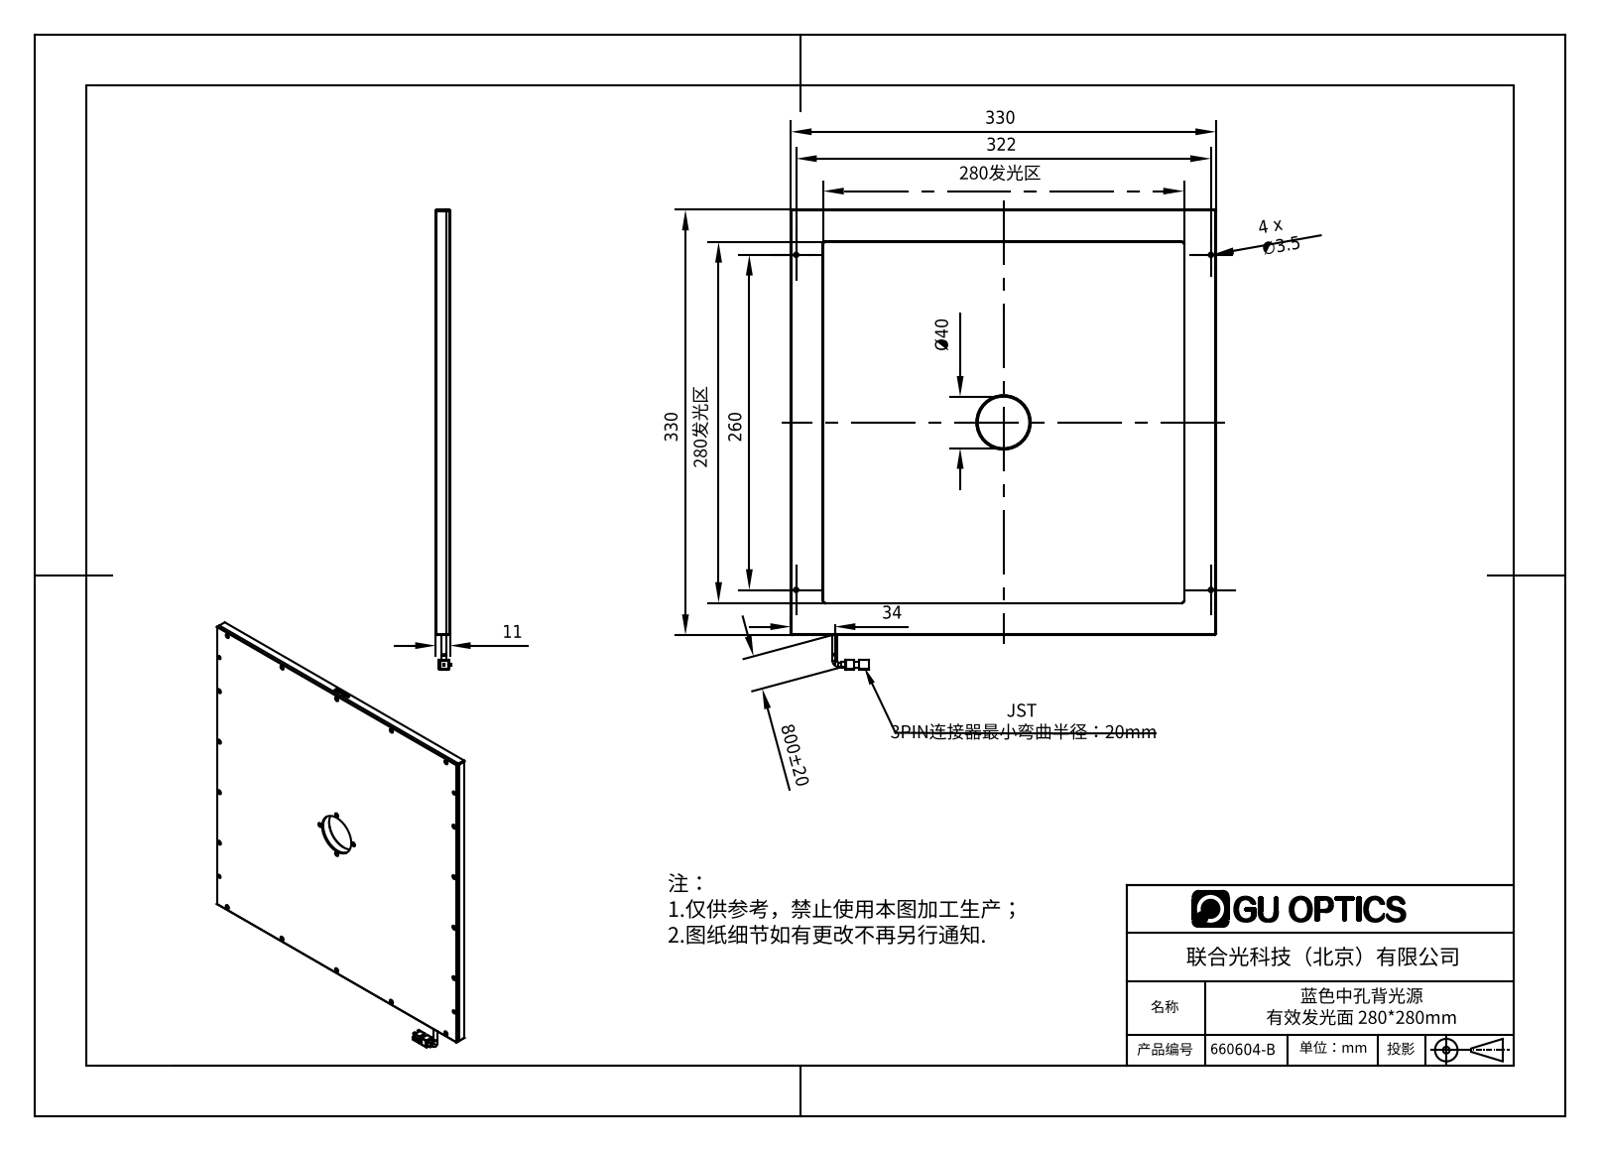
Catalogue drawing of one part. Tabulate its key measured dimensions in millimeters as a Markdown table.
| quantity | value |
| --- | --- |
| part name | 660604-B |
| STEP written by | SolidWorks 2016 (AUTOMOTIVE_DESIGN) |
| units | millimeters |
| bodies | 7 solids, 773 faces (442 planar, 178 cylindrical, 153 other) |
| overall size | 357 × 330 × 12.4 |
| volume | 1 053 000 mm³ |
| surface area | 509 529 mm² |
| round holes (diameter × count) | 2 × 22, 1.6 × 18, 2.4 × 18, 3.5 × 5, 3.6 × 4, 40 × 1, 42.2 × 1, 52 × 1 |
| round bosses / shafts (diameter × count) | 3.5 × 2, 42 × 1 |
| partial cylindrical surfaces (radius × count) | 0.5 × 8, 2 × 8, 1 × 4, 3 × 2 |
| main face-to-face distances | 6.5, 9.5, 3, 8, 1.5, 11, 2, 7.5, 322.5, 320.5 |
| hole center spacings | 322, 75, 330.62, 60, 150, 327.54, 355.22, 23 |
